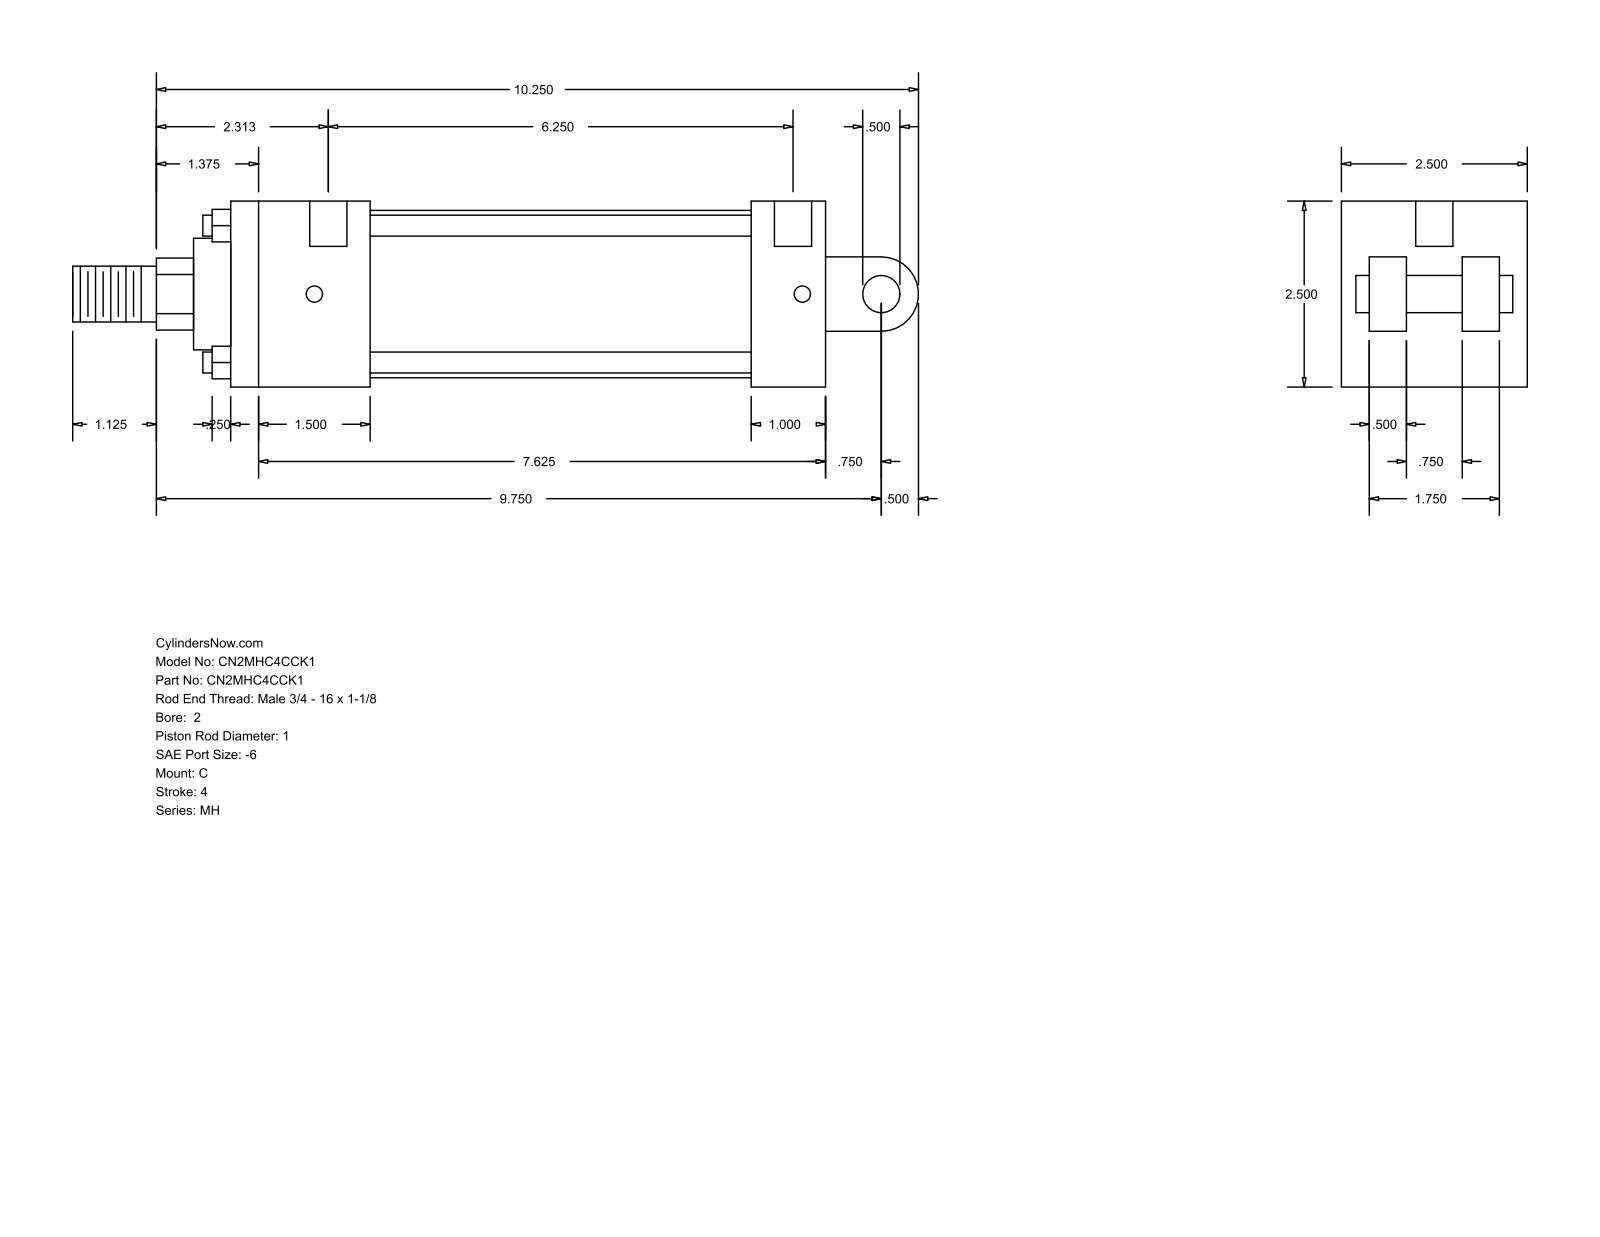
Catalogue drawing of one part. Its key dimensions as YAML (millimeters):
part_name: "MH_C__0200_1"
step_written_by: "GSSL Pune (CONFIG_CONTROL_DESIGN)"
units: millimeters
bodies: {solids: 0, faces: 99, planar: 70, cylindrical: 29, other: 0}
overall_size: [288.93, 63.5, 63.5]
round_holes:
  - {diameter: 5.56, count: 4}
  - {diameter: 12.7, count: 2}
round_bosses_or_shafts:
  - {diameter: 7.14, count: 4}
  - {diameter: 57.15, count: 1}
  - {diameter: 38.1, count: 1}
  - {diameter: 25.4, count: 1}
  - {diameter: 19.05, count: 1}
  - {diameter: 12.7, count: 1}
partial_cylinders:
  - {radius: 12.29, count: 1}
  - {radius: 12.7, count: 1}
face_to_face_distances: [63.5, 203.2, 12.7, 25.4, 47.63, 53.98, 9.52, 177.8, 130.17, 155.57]
hole_center_spacings: [166.68, 3.17, 4.76, 158.75, 161.92, 163.51]
